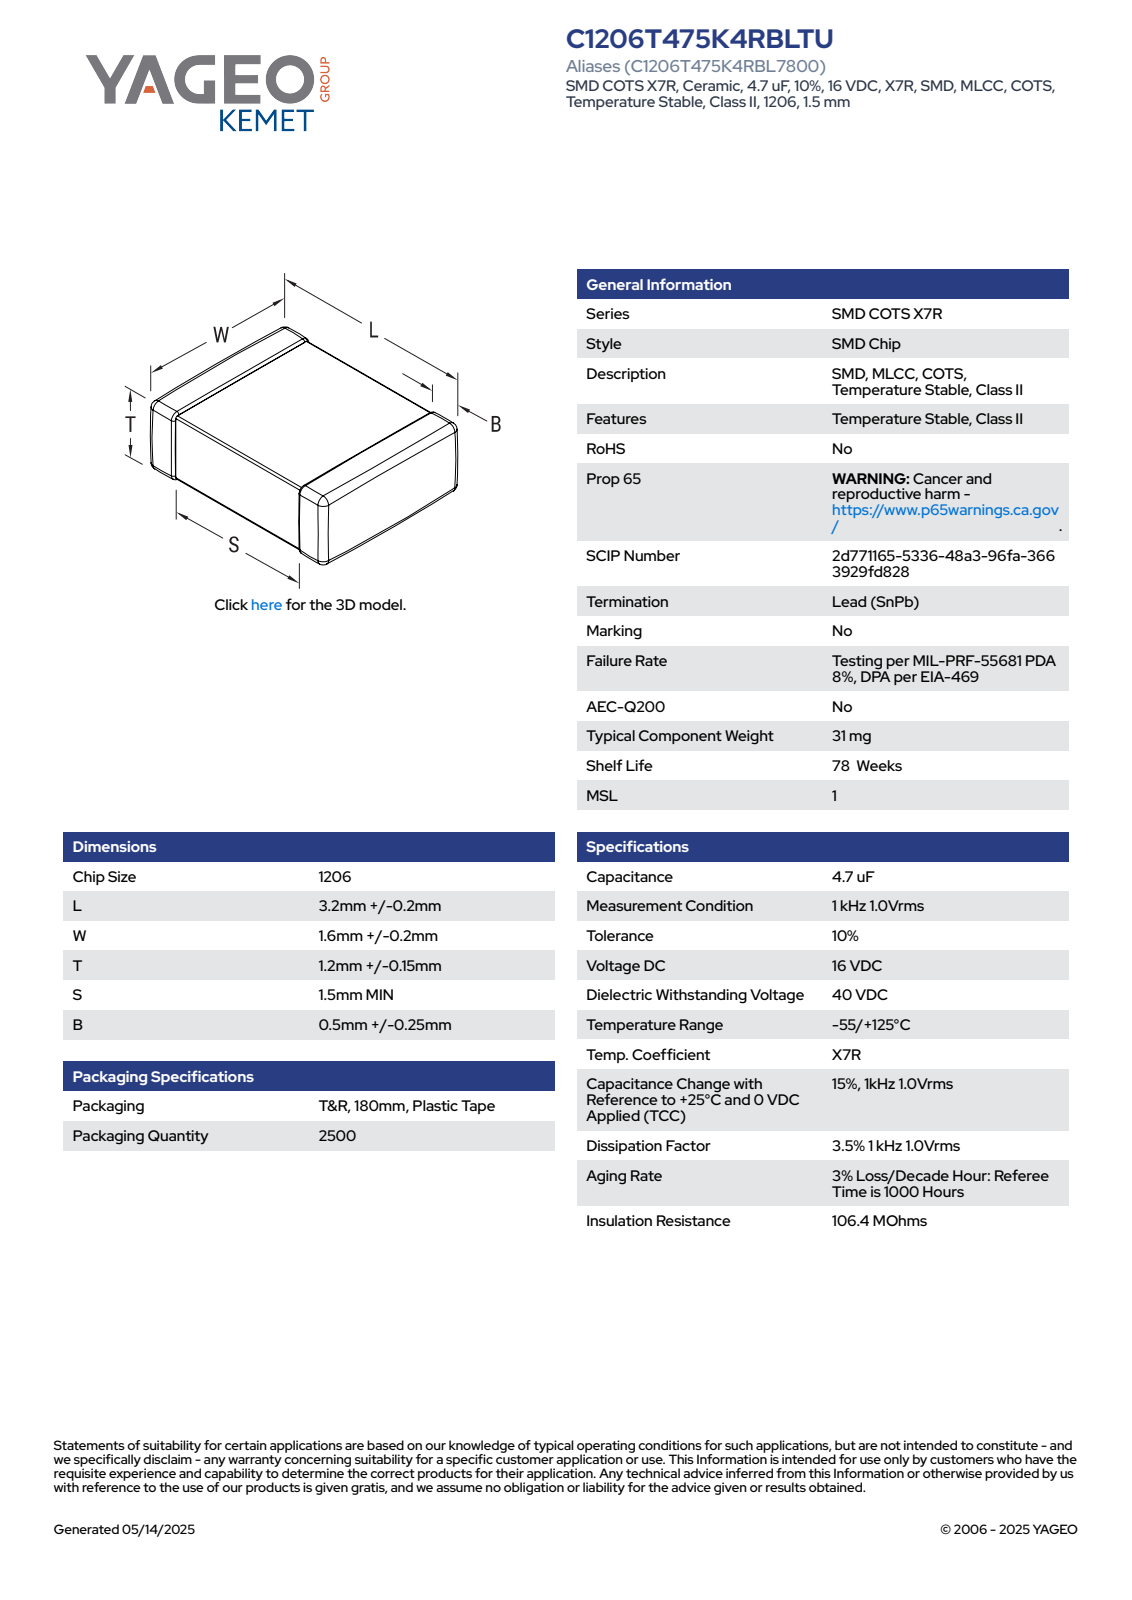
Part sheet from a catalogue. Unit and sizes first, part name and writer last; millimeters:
Units: millimetres
Overall size (bounding box): 3.4 × 1.8 × 1.35
Main face-to-face distances: 1.31, 1.76, 1.27, 1.35, 1.72, 3.4, 1.8, 1.32, 1.28, 1.57
Volume: 8 mm³ · Surface area: 26 mm²
Bodies: 4 solids, 125 faces (71 planar, 38 cylindrical, 16 other)
Part name (STEP PRODUCT): CCSM_STD_1206_L3.4W1.8T1.35S1.2B0.75
STEP written by: SolidWorks 2021 (AUTOMOTIVE_DESIGN)
